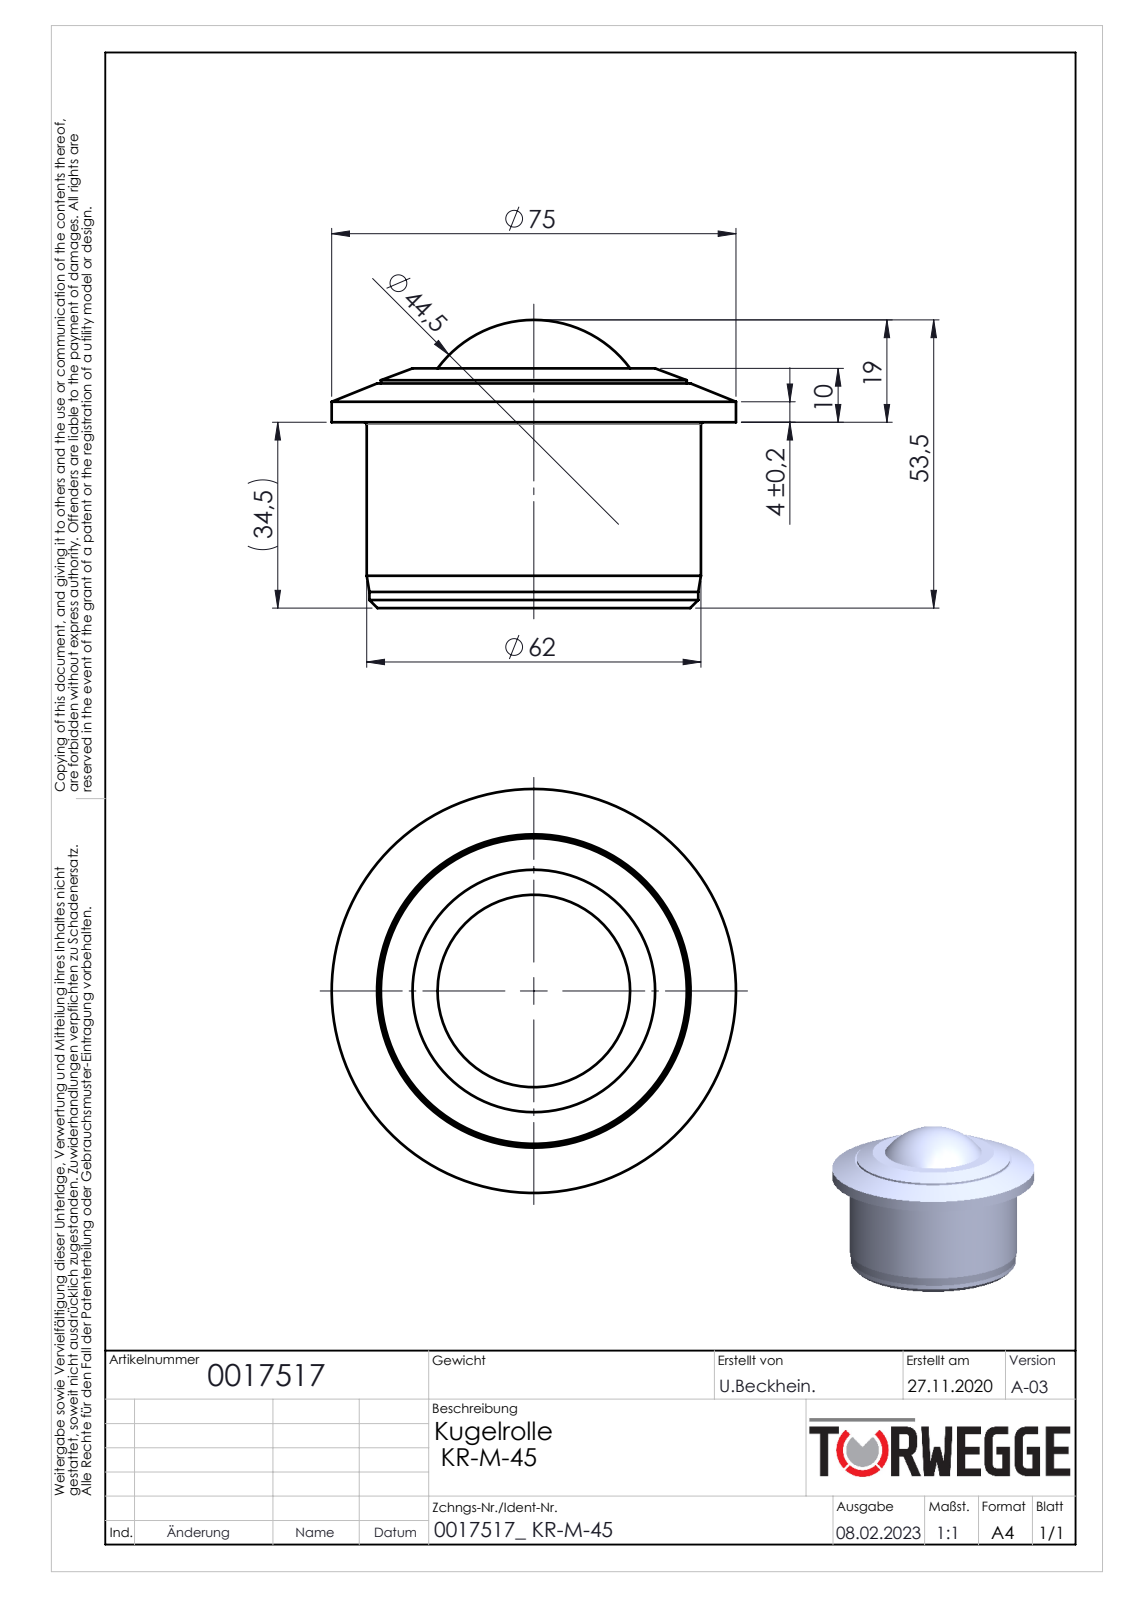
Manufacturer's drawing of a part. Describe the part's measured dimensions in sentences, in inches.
The part is named "0017517". Its 3-D file was written by "SolidWorks 2018 (AUTOMOTIVE_DESIGN)". It is 1 solid with 27 faces: 5 planar, 10 cylindrical and 12 other. Overall it measures 2.953 by 2.953 by 2.106 inches. Its volume is 8.732 cubic inches and its surface area 26.01 square inches. Round holes: 1 of diameter 2.252. Round bosses or shafts: 1 of diameter 2.953, 1 of diameter 2.441, 1 of diameter 2.402, 1 of diameter 2.234. The main face-to-face distances are 1.358, 1.752, 0.394, 1.642, 0.283, 0.11, 1.634, 0.276, 0.118.
